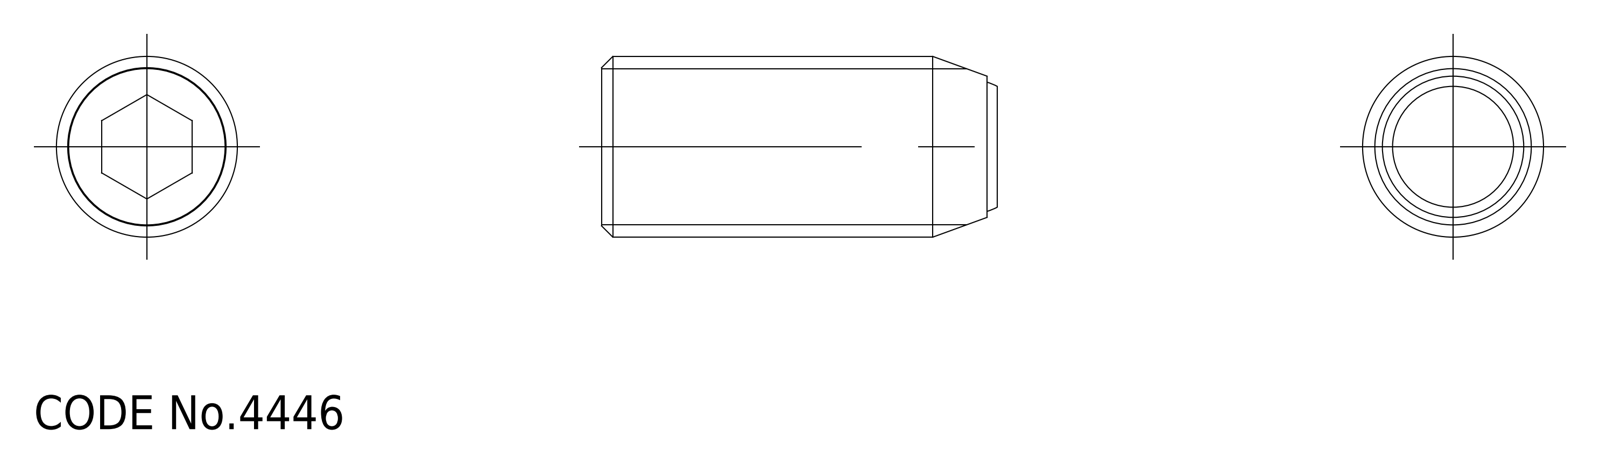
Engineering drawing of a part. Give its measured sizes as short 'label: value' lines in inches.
name: ball; SCS_M16_35_F_16676_36
written by: CADfix (AUTOMOTIVE_DESIGN)
unit: in
bodies: 2 solids, 20 faces (0 planar, 0 cylindrical, 20 other)
size: 1.432 × 0.63 × 0.63
volume: 0.35 in³; area: 4.76 in²
